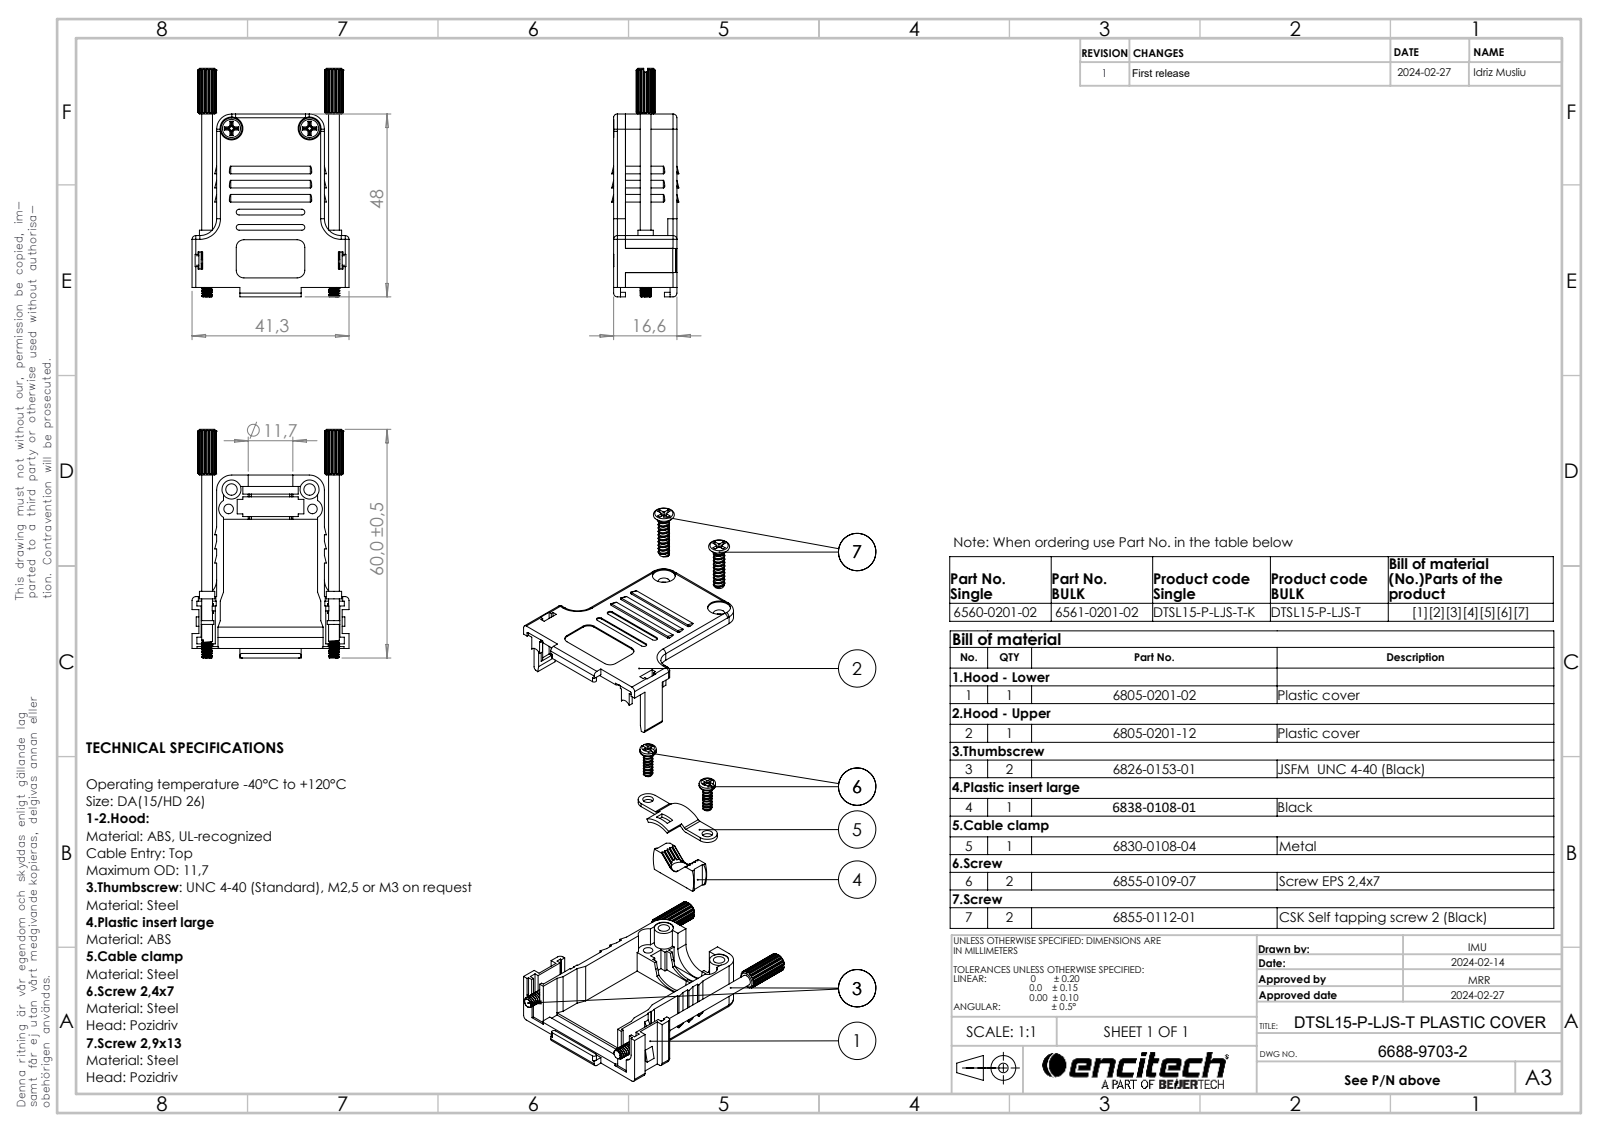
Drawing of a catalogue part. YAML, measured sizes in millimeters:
part_name: "6855-0112-02; 6838-0108-01; 6805-0201-02; 6830-0108-04 (+4 more)"
step_written_by: "SolidWorks 2021 (AUTOMOTIVE_DESIGN)"
units: millimeters
bodies: {solids: 10, faces: 963, planar: 557, cylindrical: 320, other: 86}
overall_size: [60, 41.2, 17.6]
volume: 11763
surface_area: 14651
round_holes:
  - {diameter: 2.5, count: 2}
  - {diameter: 2.8, count: 2}
  - {diameter: 3, count: 2}
  - {diameter: 5, count: 2}
  - {diameter: 6, count: 2}
  - {diameter: 4.6, count: 1}
round_bosses_or_shafts:
  - {diameter: 4.3, count: 2}
  - {diameter: 4, count: 2}
  - {diameter: 3.5, count: 2}
  - {diameter: 2.84, count: 2}
  - {diameter: 2.8, count: 2}
  - {diameter: 2.46, count: 2}
  - {diameter: 2.02, count: 2}
partial_cylinders:
  - {radius: 0.35, count: 27}
  - {radius: 1, count: 18}
  - {radius: 2, count: 7}
  - {radius: 0.75, count: 6}
  - {radius: 0.5, count: 4}
  - {radius: 2.3, count: 4}
  - {radius: 0.25, count: 2}
  - {radius: 0.6, count: 2}
face_to_face_distances: [2.4, 11.9, 14.3, 16.6, 14.2, 2.3, 1.8, 0.8, 6.45, 32.95]
hole_center_spacings: [5.15, 21.85, 10.78, 10.97, 11.26, 11.41, 20.5, 22]
